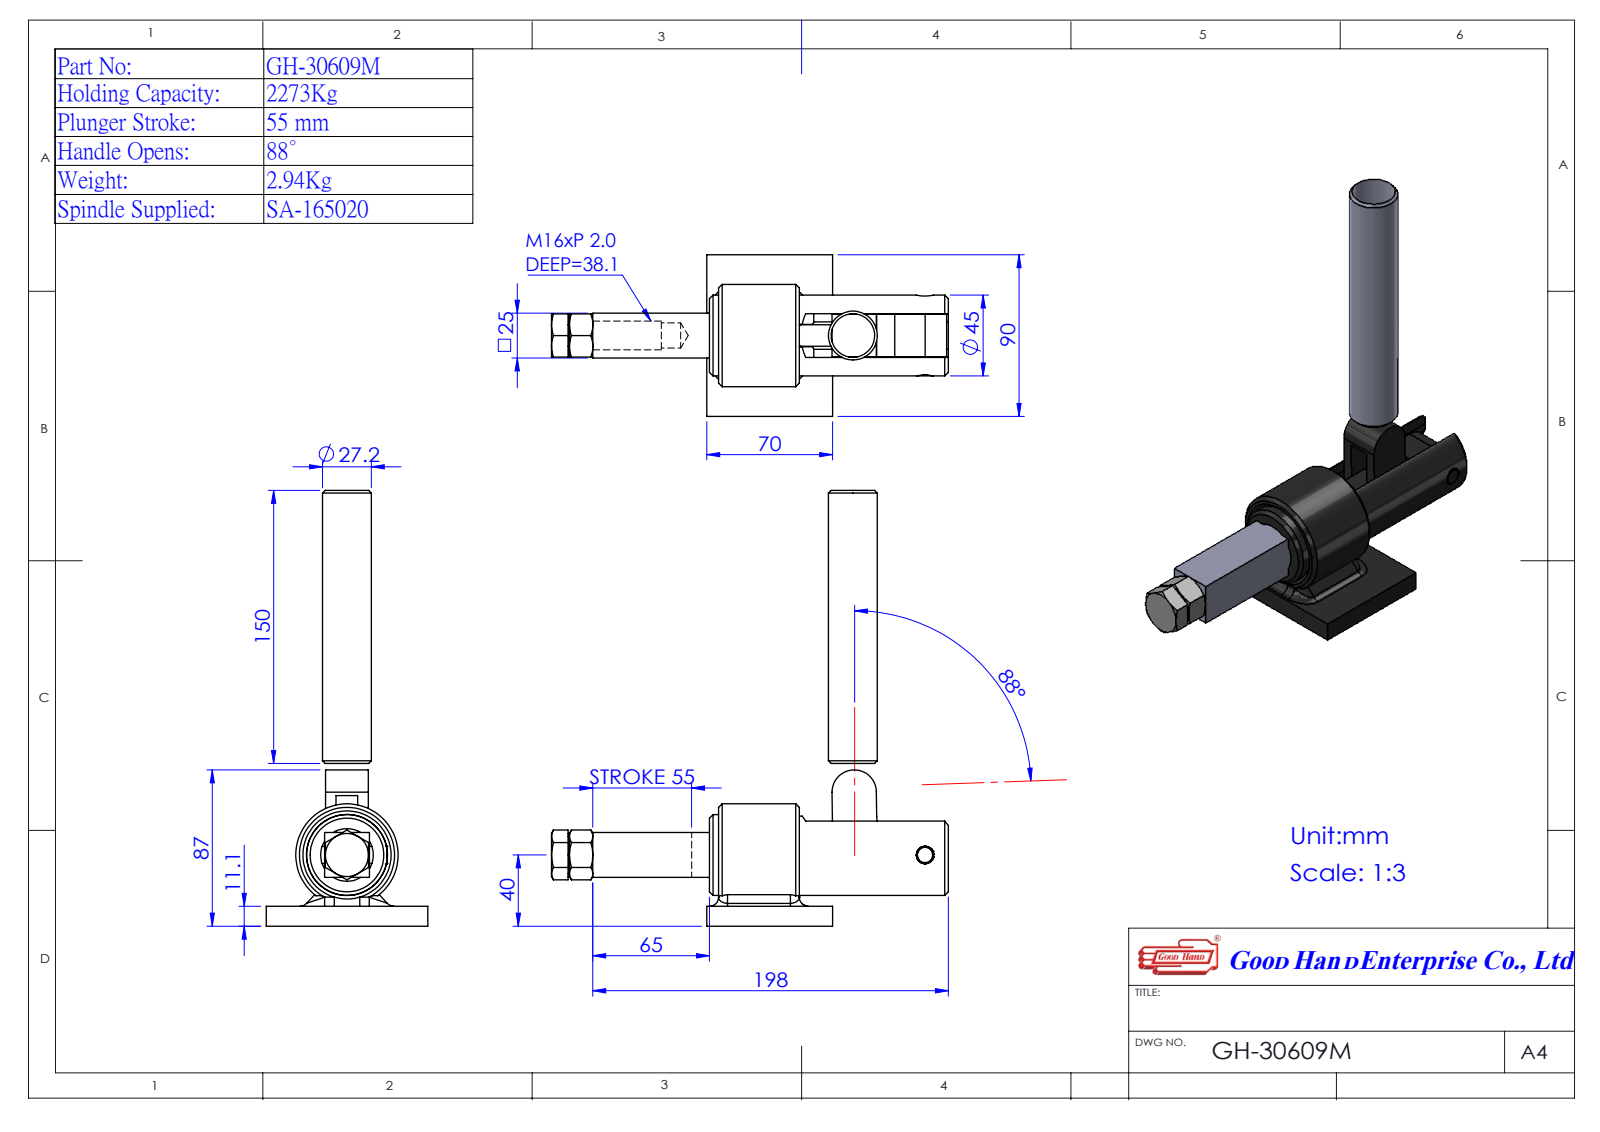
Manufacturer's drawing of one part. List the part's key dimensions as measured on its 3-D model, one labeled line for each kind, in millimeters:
Part name (STEP PRODUCT): 43060905 [連桿30609]-1^GH-30609M(簡化); Group1^GH-30609M(簡化); Group6^GH-30609M(簡化); Group7^GH-30609M(簡化) (+4 more)
STEP written by: SolidWorks 2016 (AUTOMOTIVE_DESIGN)
Units: millimetres
Bodies: 8 solids, 387 faces (176 planar, 58 cylindrical, 153 other)
Overall size (bounding box): 242.34 × 220.21 × 90
Volume: 382 377 mm³ · Surface area: 126 268 mm²
Round holes (diameter × count): ⌀7.5 ×3, ⌀14 ×1, ⌀21.7 ×1, ⌀45 ×1
Round bosses / shafts (diameter × count): ⌀57 ×1, ⌀27.2 ×1, ⌀24 ×1, ⌀16 ×1
Partial cylindrical surfaces — rounded edges, fillets, slot ends (radius × count): R0.72 ×5, R1.52 ×5, R5 ×4, R2 ×2, R10 ×2, R12 ×2, R12.5 ×2, R7.5 ×1
Main face-to-face distances: 25, 6.5, 18.5, 11.1, 24.4, 0.6, 5.9, 17.9, 27.1, 16
Hole centre spacings: 39.24, 52.68, 91.91
